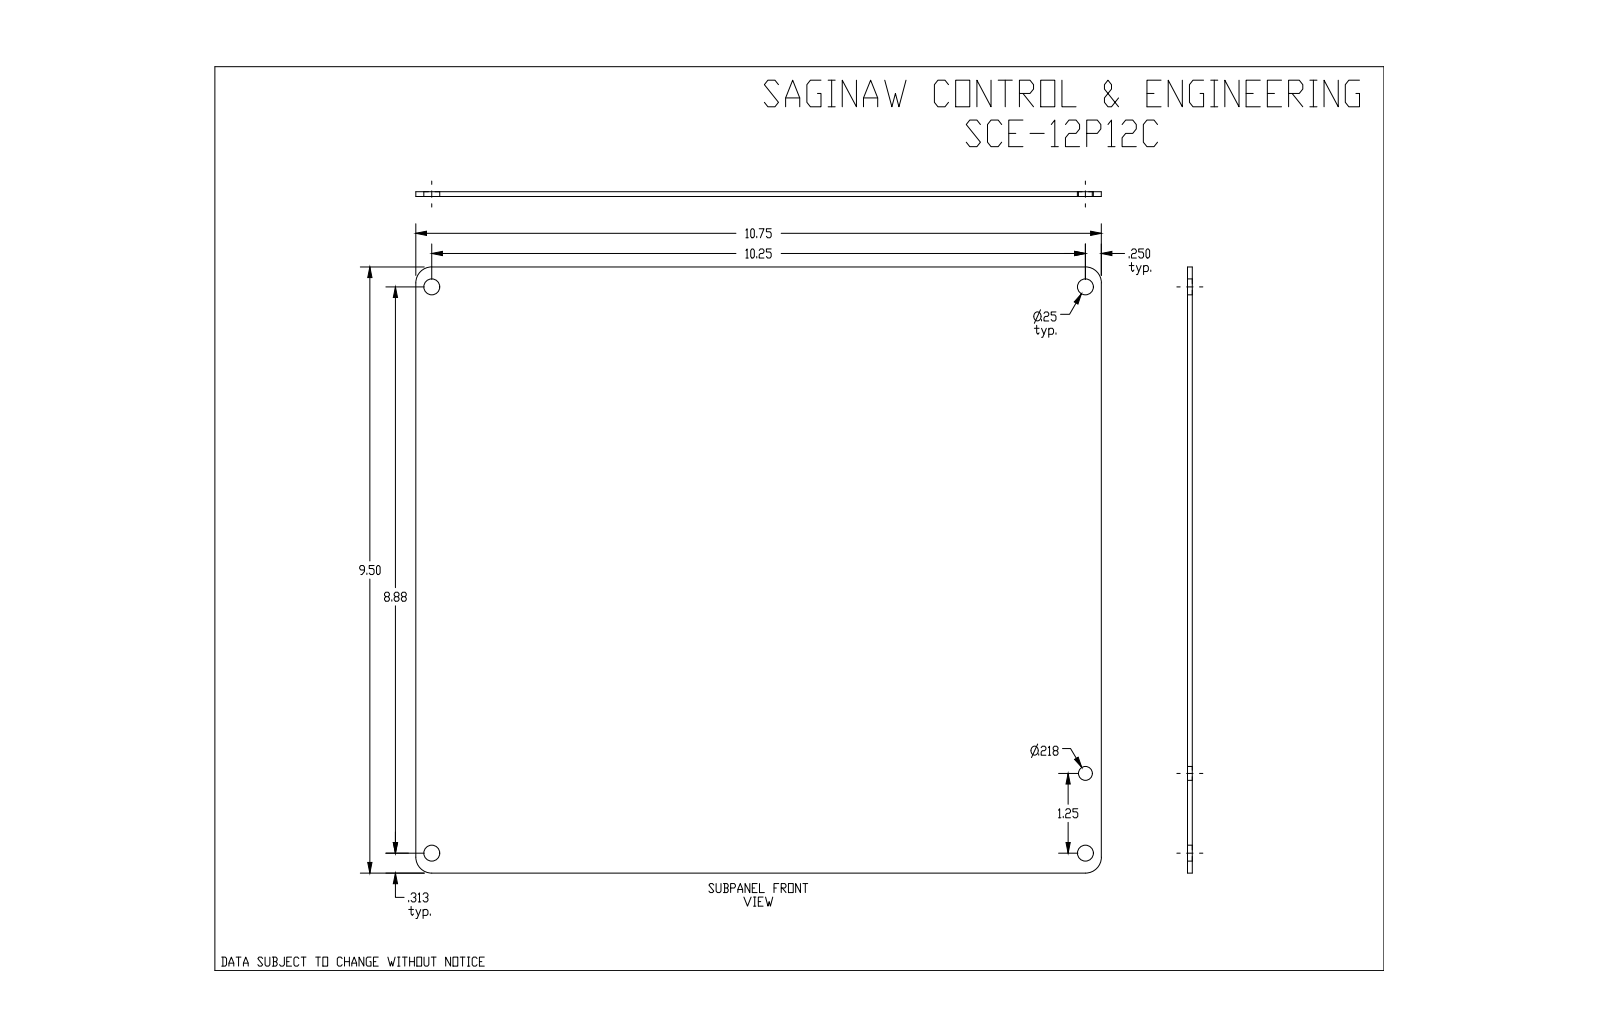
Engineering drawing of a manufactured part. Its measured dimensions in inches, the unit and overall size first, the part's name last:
Units: inches
Overall size (bounding box): 10.75 × 9.5 × 0.075
Round holes (diameter × count): ⌀0.25 ×4, ⌀0.218 ×1
Partial cylindrical surfaces — rounded edges, fillets, slot ends (radius × count): R0.25 ×4
Main face-to-face distances: 0.075, 9.5, 10.75
Hole centre spacings: 8.875, 10.25, 13.558, 1.25, 7.625, 10.326, 12.775
Volume: 7.638 in³ · Surface area: 207 in²
Bodies: 1 solid, 15 faces (6 planar, 9 cylindrical, 0 other)
Part name (STEP PRODUCT): SCE-12P12C
STEP written by: SolidWorks 2019 (CONFIG_CONTROL_DESIGN)
